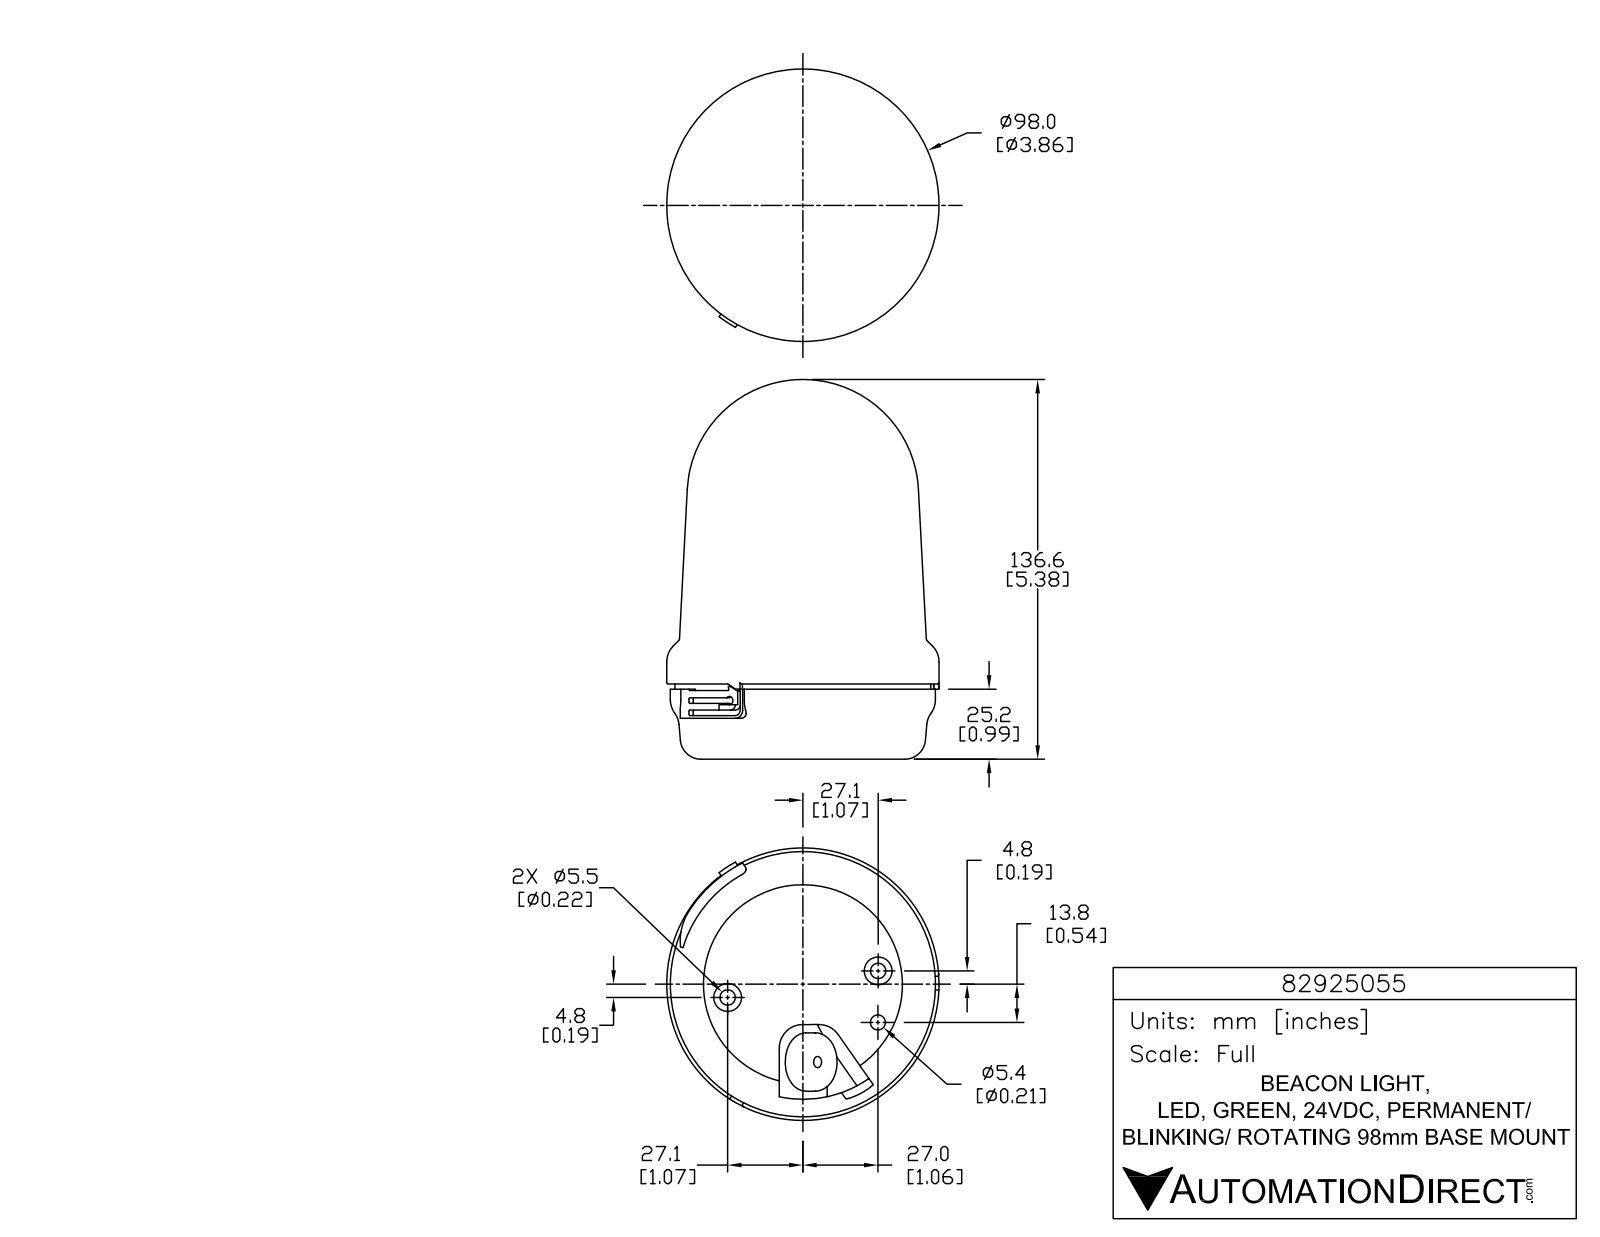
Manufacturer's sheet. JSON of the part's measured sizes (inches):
{"part_name": "82925055", "step_written_by": "SolidWorks 2015 (AUTOMOTIVE_DESIGN)", "units": "inches", "bodies": {"solids": 1, "faces": 872, "planar": 566, "cylindrical": 204, "other": 102}, "overall_size": [5.378, 3.858, 3.858], "volume_in3": 44.69, "surface_area_in2": 73.66, "round_holes": [[0.059, 3], [0.217, 2], [0.157, 1], [0.213, 1], [2.819, 1]], "round_bosses_or_shafts": [[0.339, 3], [0.084, 3], [0.394, 2], [3.858, 1], [3.756, 1], [3.626, 1], [0.827, 1]], "partial_cylinders_radius": [[0.005, 9], [0.005, 6], [0.012, 6], [0.012, 6], [0.012, 6], [0.196, 6], [0.02, 5], [0.039, 4]], "face_to_face_distances": [1.045, 0.972, 0.073, 0.02, 0.992, 1.065, 0.236, 0.579, 0.559, 0.413], "hole_center_spacings": [1.083, 0.73, 1.193, 2.158, 2.165]}
